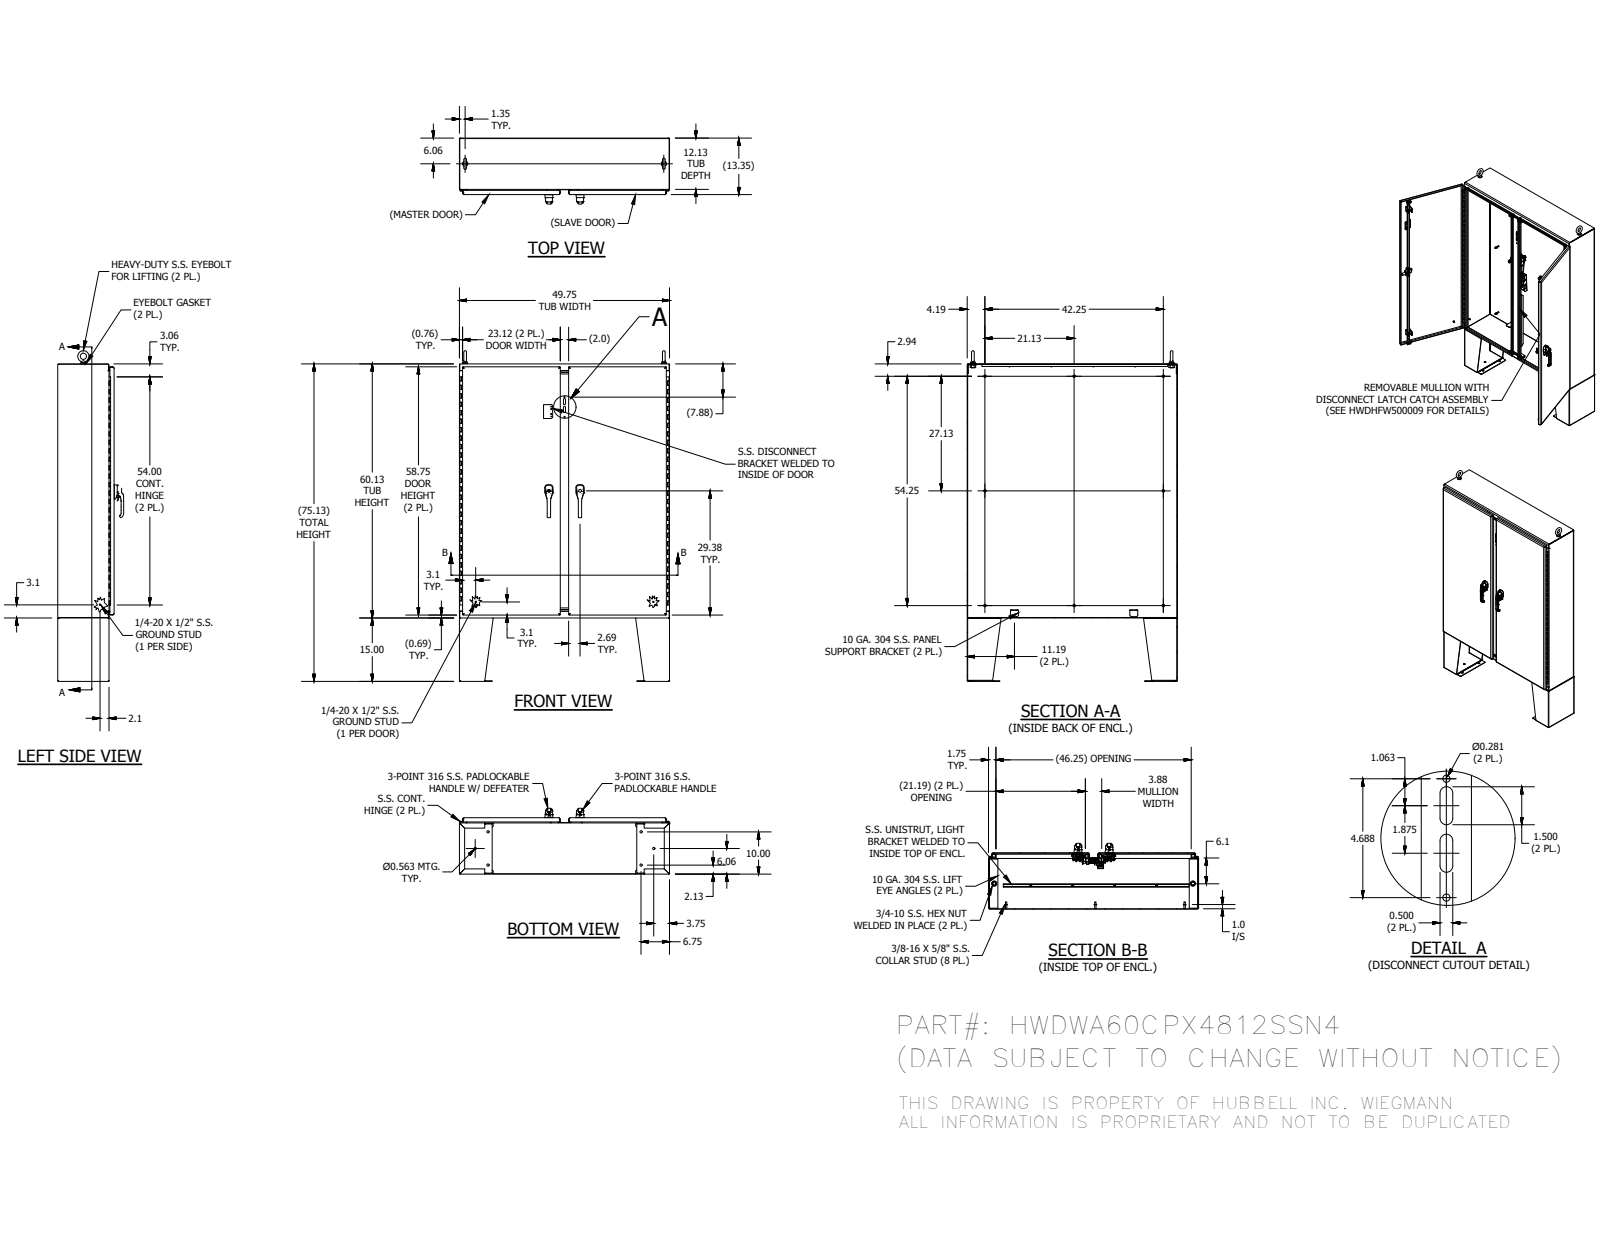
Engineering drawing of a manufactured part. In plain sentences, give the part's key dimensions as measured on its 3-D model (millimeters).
The part is named "WA60CPX4812SSN4BLR; WACPX4812SSN4TOP; WACPX4812SSN4BTM; HFW303115 (+8 more)". Its 3-D file was written by "Autodesk Inventor 2016 (AUTOMOTIVE_DESIGN)". It is 212 solids with 8742 faces: 4041 planar, 2945 cylindrical and 1756 other. Overall it measures 1987.49 by 1263.65 by 396.15 millimeters. Its volume is 20 330 000 cubic millimeters and its surface area 15 340 000 square millimeters. Round holes: 20 of diameter 6.35, 18 of diameter 9.52, 18 of diameter 14.29, 12 of diameter 4.98, 10 of diameter 7.14, 9 of diameter 4.76, 8 of diameter 6.65, 6 of diameter 3.96, 6 of diameter 4.83, 6 of diameter 5.4, 6 of diameter 7.33, 6 of diameter 7.37. Round bosses or shafts: 16 of diameter 8.38, 16 of diameter 6.35, 14 of diameter 15.88, 9 of diameter 14.29, 9 of diameter 9.52, 9 of diameter 8.56, 6 of diameter 25.4, 6 of diameter 12.7. Partial cylindrical surfaces (rounded edges, fillets, slot ends): 358 of radius 0.5, 222 of radius 0.3, 144 of radius 0.51, 58 of radius 3.17, 42 of radius 0.47, 28 of radius 1.27, 28 of radius 2, 23 of radius 6.35. The main face-to-face distances are 2.64, 336.39, 333.75, 339.03, 1261, 1524.54, 3.17, 305.33, 31.06, 0.53. The hole center spacings are 9.65, 19.31, 22.5, 30.36, 31.38, 37.06, 51.83, 88.97.
